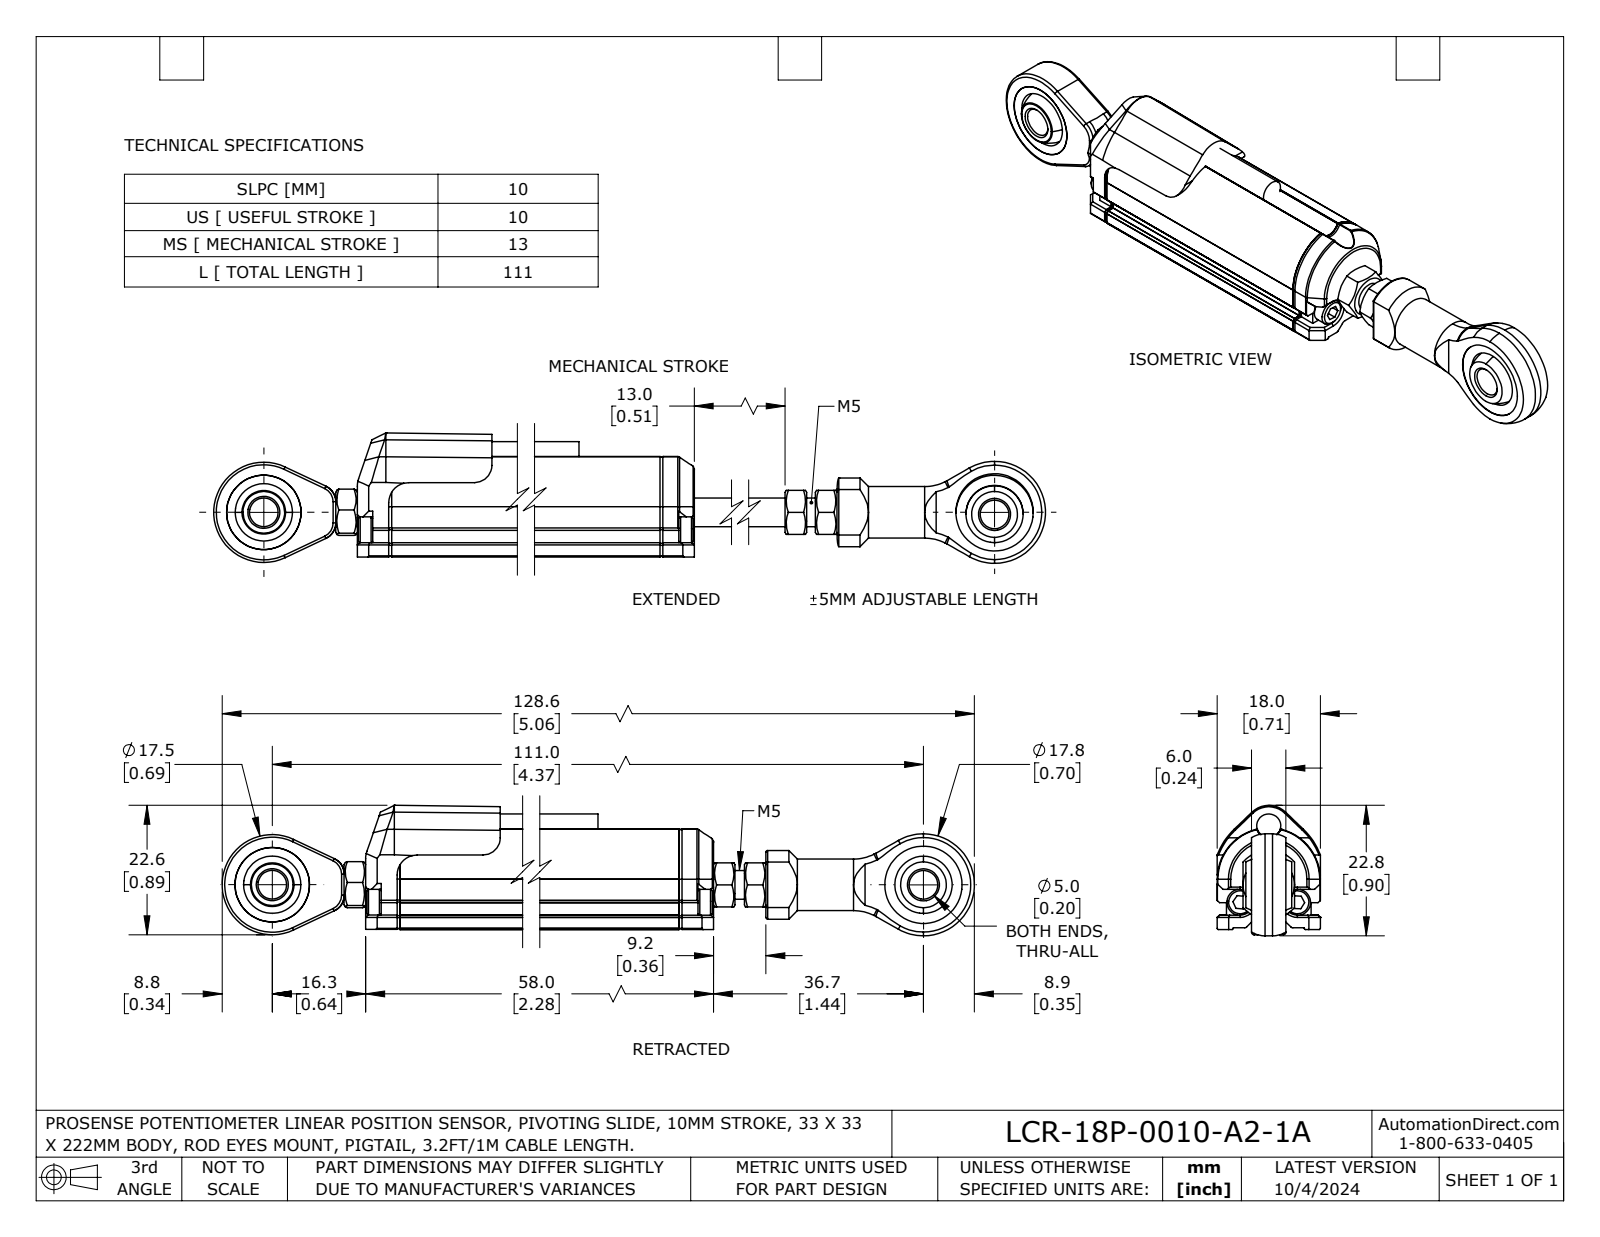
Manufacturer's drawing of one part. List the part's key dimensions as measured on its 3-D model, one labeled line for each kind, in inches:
Part name (STEP PRODUCT): LCR-18P-0010-A2-1A
STEP written by: SolidWorks 2023 (AUTOMOTIVE_DESIGN)
Units: inches
Bodies: 9 solids, 542 faces (306 planar, 146 cylindrical, 90 other)
Overall size (bounding box): 5.065 × 0.896 × 0.709
Volume: 2.062 in³ · Surface area: 25.49 in²
Round holes (diameter × count): ⌀0.197 ×3, ⌀0.394 ×2, ⌀0.213 ×1, ⌀0.272 ×1, ⌀0.531 ×1
Round bosses / shafts (diameter × count): ⌀0.113 ×4, ⌀0.354 ×1, ⌀0.197 ×1, ⌀0.165 ×1
Partial cylindrical surfaces — rounded edges, fillets, slot ends (radius × count): R0.008 ×12, R0.004 ×10, R0.02 ×8, R0.012 ×6, R0.018 ×6, R0.016 ×4, R0.039 ×4, R0.043 ×4
Main face-to-face distances: 0.236, 1.811, 0.709, 0.059, 0.173, 0.472, 0.071, 0.063, 0.646, 0.409
Hole centre spacings: 4.37
